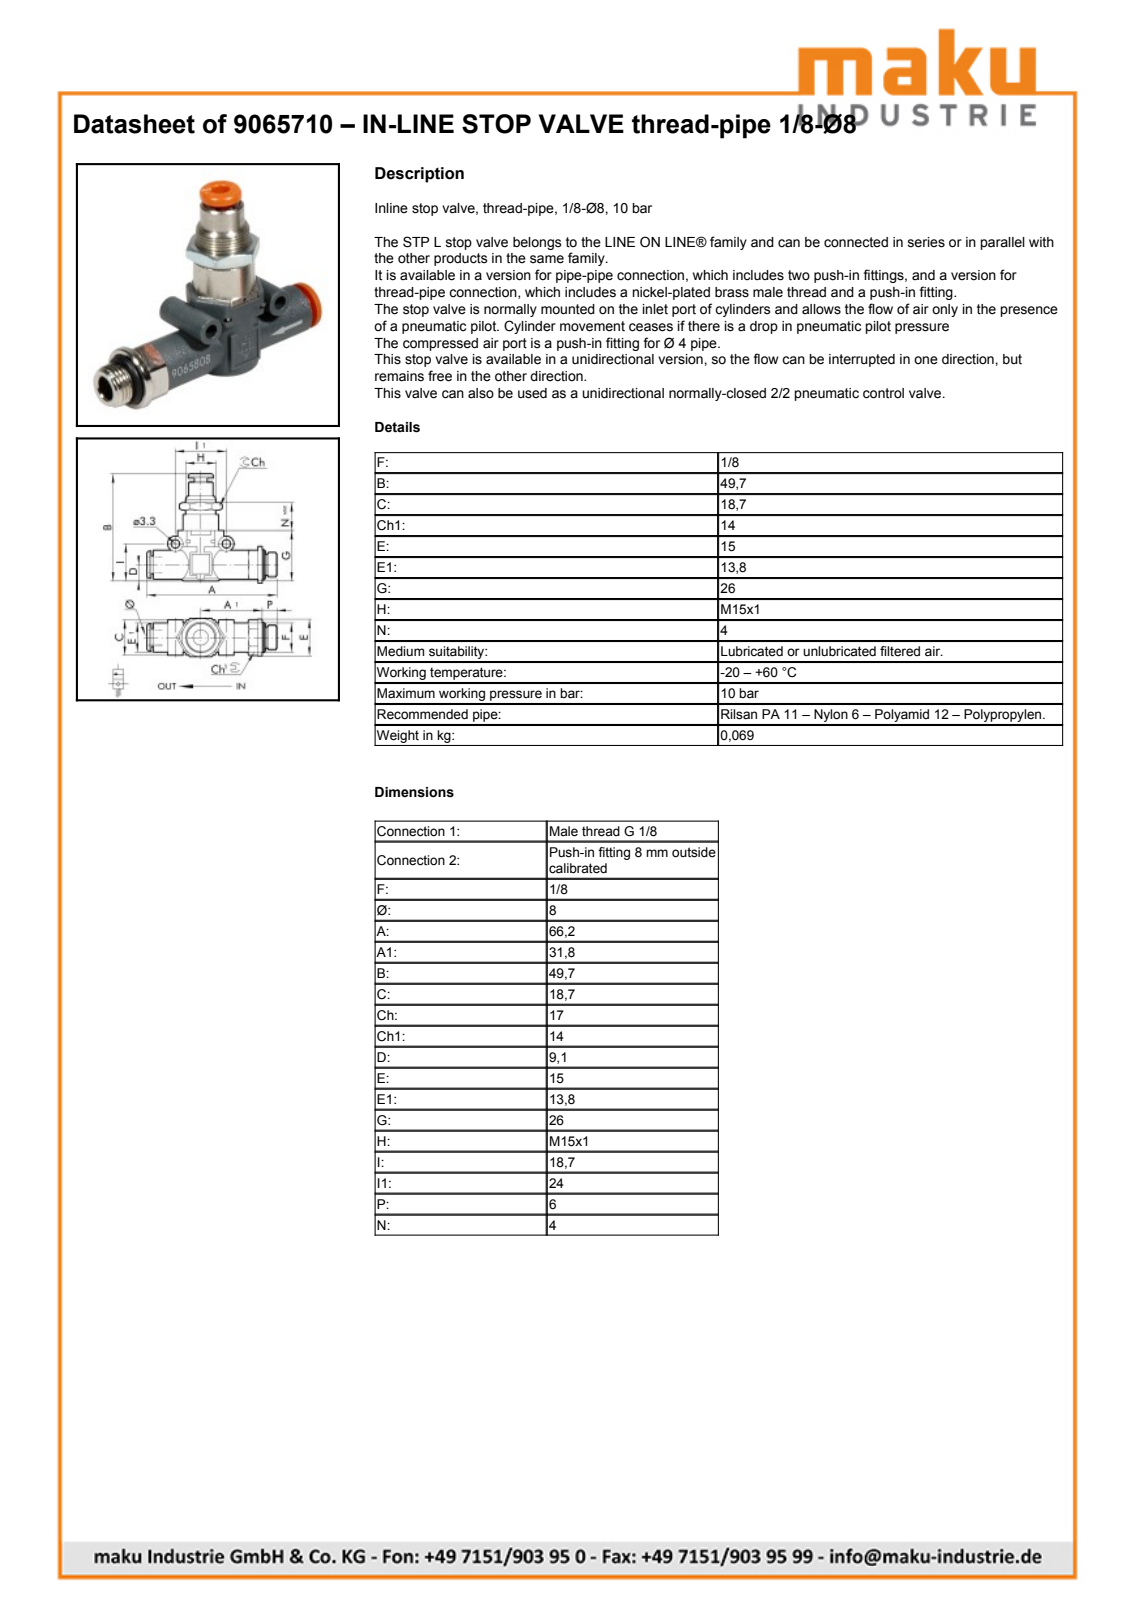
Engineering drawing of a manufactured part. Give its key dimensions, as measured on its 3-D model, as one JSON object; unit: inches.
{"part_name": "9065710; LINE-ON-LINE D8 PNV_L-body; LINE-ON-LINE D8-1/8 RML-thread port; LINE-ON-LINE D8 VNR-L bushing (+2 more)", "step_written_by": "PARTsolutions (AUTOMOTIVE_DESIGN)", "units": "inches", "bodies": {"solids": 5, "faces": 197, "planar": 122, "cylindrical": 59, "other": 16}, "overall_size": [2.606, 1.957, 0.736], "volume_in3": 0.771, "surface_area_in2": 17.11, "round_holes": [[0.13, 2], [0.236, 2], [0.138, 1], [0.197, 1], [0.218, 1], [0.244, 1], [0.319, 1], [0.433, 1], [0.459, 1], [0.492, 1], [0.591, 1]], "round_bosses_or_shafts": [[0.283, 2], [0.236, 2], [0.74, 1], [0.709, 1], [0.591, 1], [0.543, 1], [0.535, 1], [0.504, 1]], "partial_cylinders_radius": [[0.148, 1], [0.313, 1], [0.407, 1], [0.451, 1]], "face_to_face_distances": [0.949, 1.693, 0.161, 0.787, 0.728, 0.807, 1.854, 0.906, 0.866, 0.551], "hole_center_spacings": [0.605, 0.945]}
